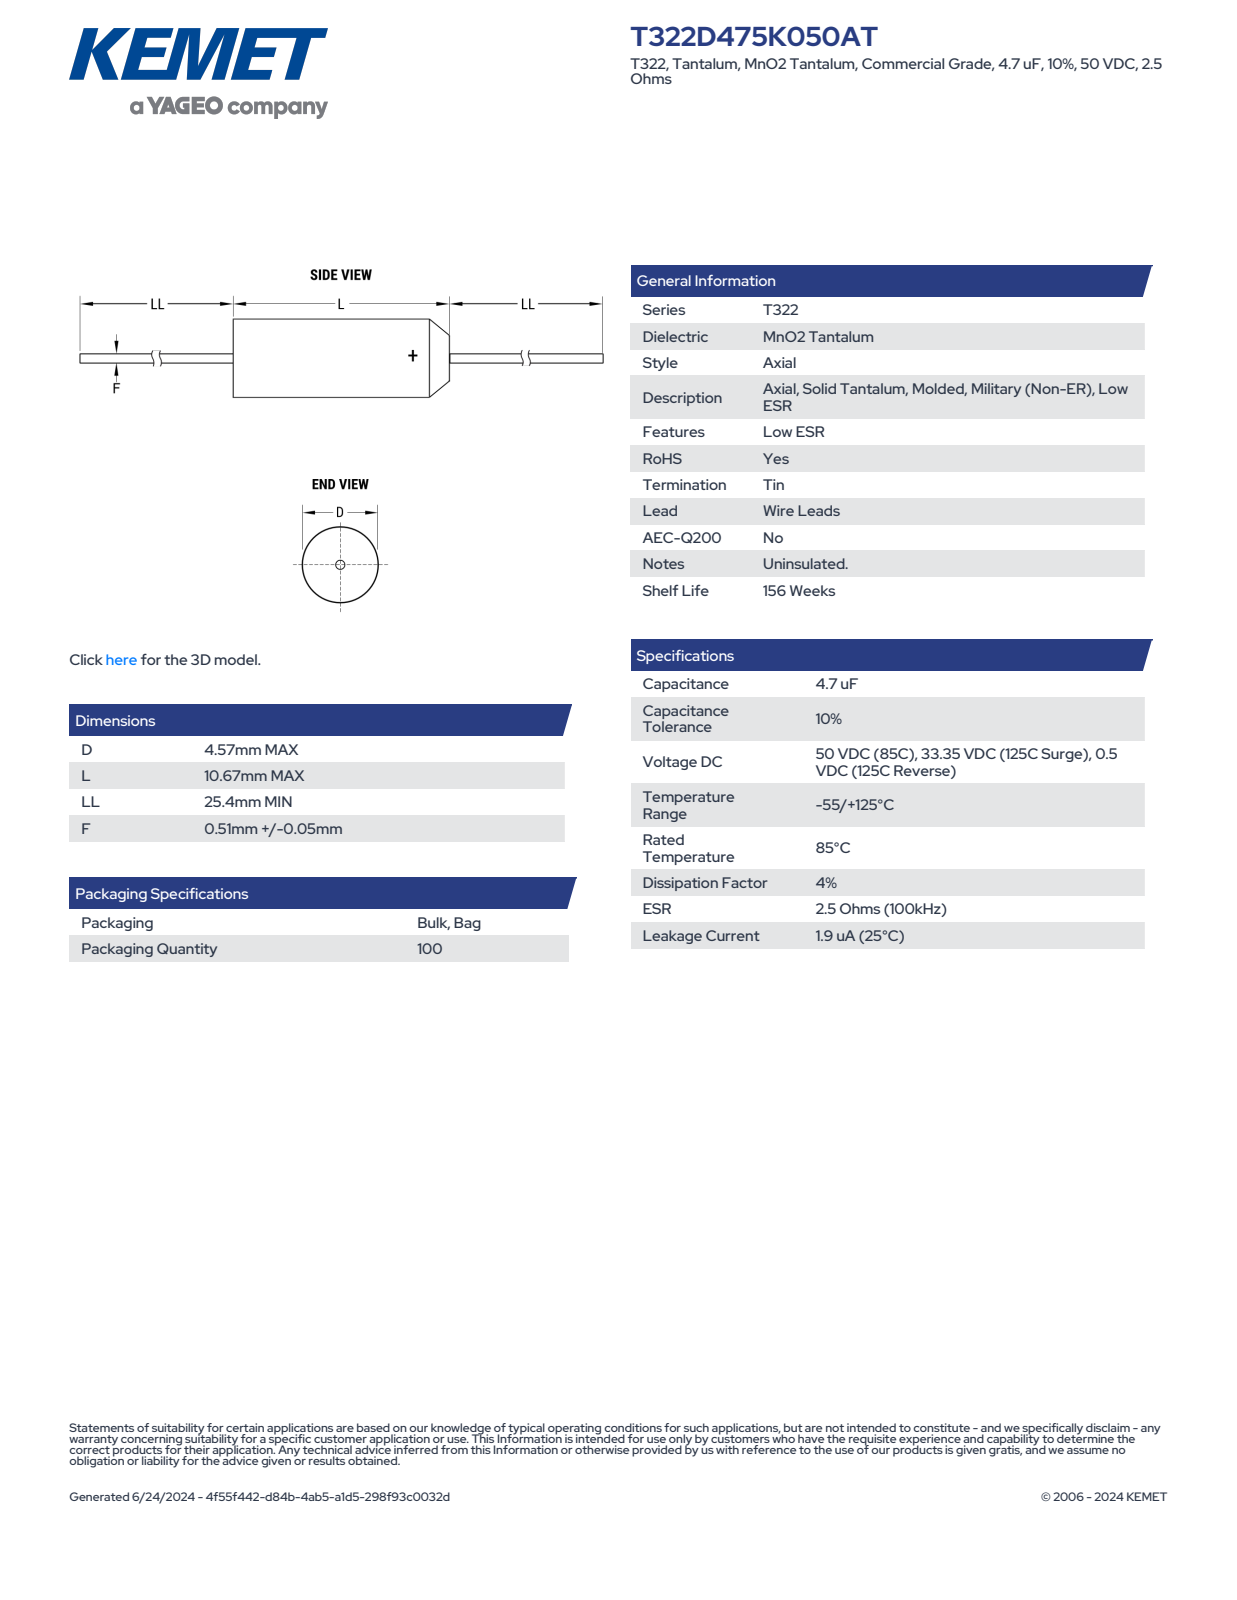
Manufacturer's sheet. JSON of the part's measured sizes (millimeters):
{"part_name": "CTAM_D4.57L10.67LL25.4F0.56", "step_written_by": "SolidWorks 2020 (AUTOMOTIVE_DESIGN)", "units": "millimeters", "bodies": {"solids": 1, "faces": 102, "planar": 38, "cylindrical": 25, "other": 39}, "overall_size": [61.47, 4.57, 4.57], "volume_mm3": 184, "surface_area_mm2": 268, "round_bosses_or_shafts": [[4.57, 1], [0.56, 1]], "partial_cylinders_radius": [[2.27, 1]], "face_to_face_distances": [10.67, 25.4, 36.07, 61.47, 34.47, 9.07, 1.6, 27, 34.37, 8.97]}
